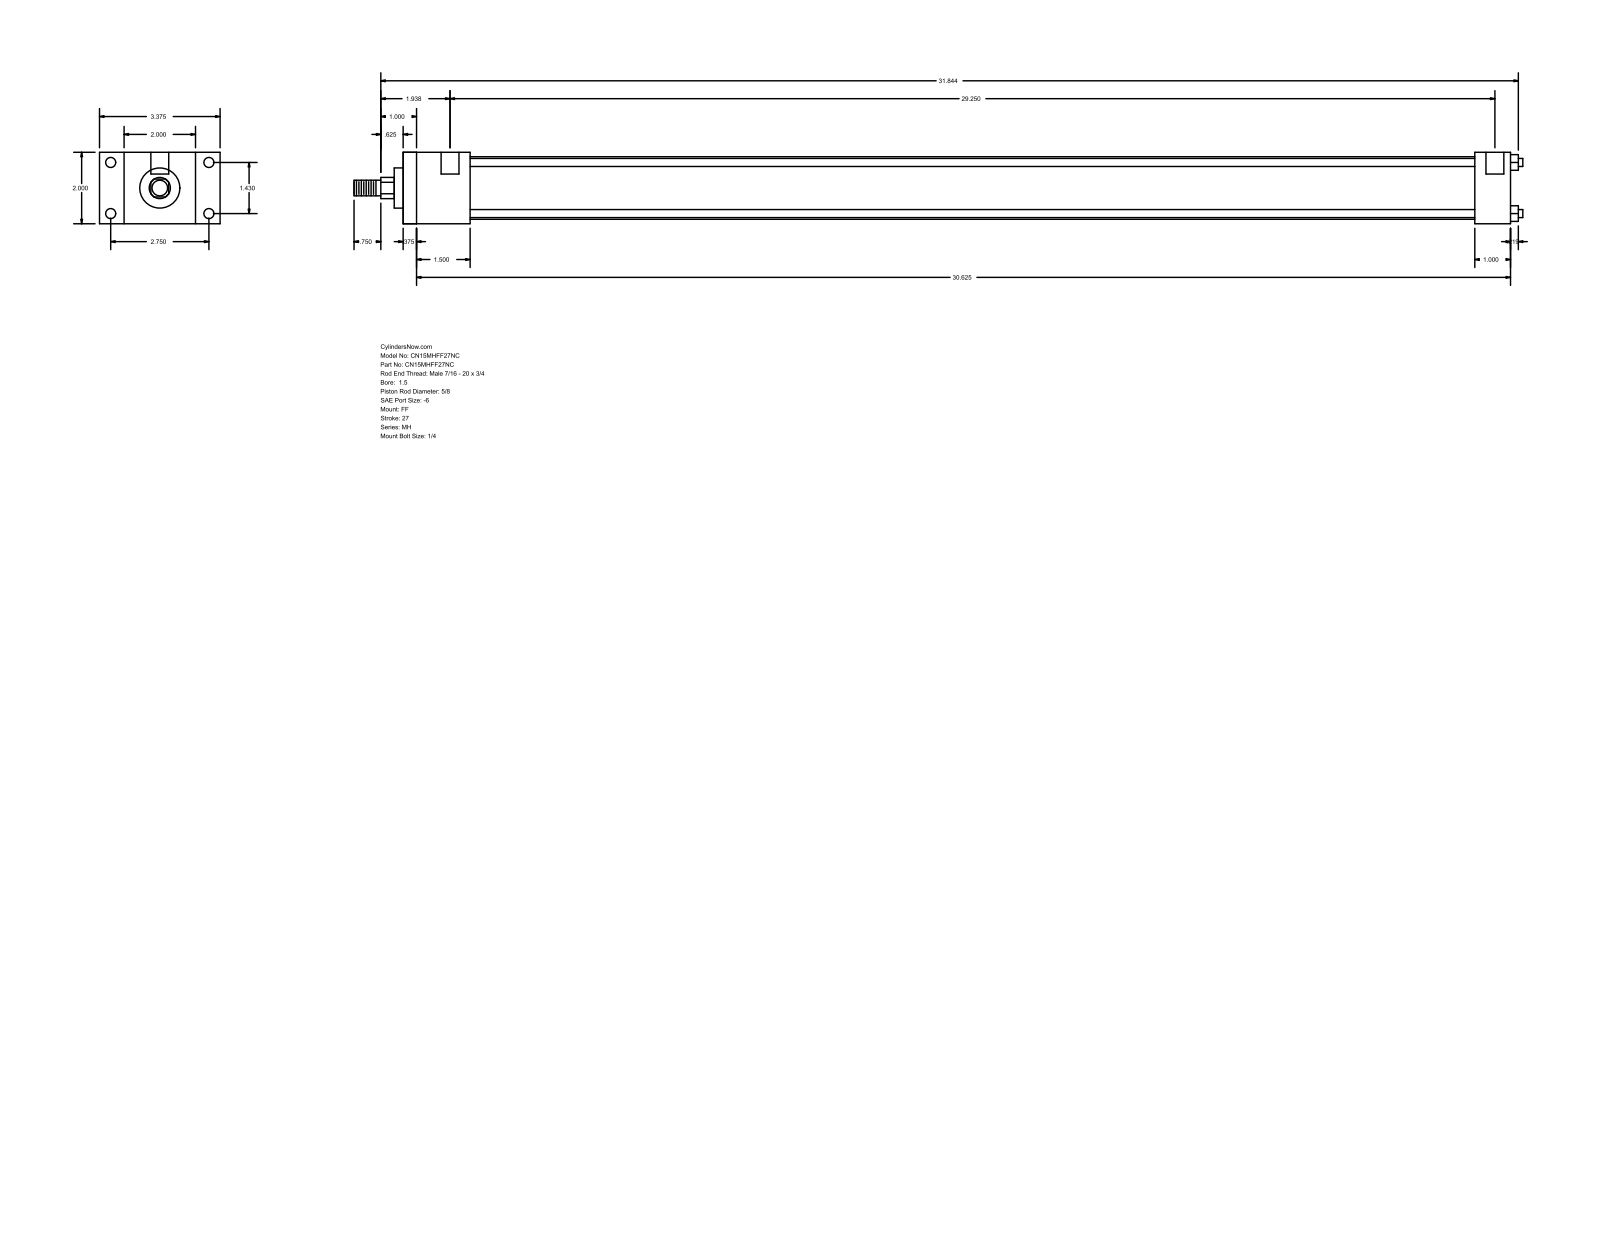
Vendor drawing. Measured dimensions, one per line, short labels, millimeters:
name: MH_FF__0150_0.625
written by: GSSL Pune (CONFIG_CONTROL_DESIGN)
unit: mm
bodies: 0 solids, 92 faces (64 planar, 28 cylindrical, 0 other)
size: 831.06 × 85.72 × 50.8
holes: 4× ⌀5.56, 4× ⌀7.14, 2× ⌀12.7
bosses: 4× ⌀5.71, 1× ⌀44.45, 1× ⌀28.57, 1× ⌀15.88, 1× ⌀11.11
rounds: 1× R7.54
face distances: 50.8, 787.39, 9.52, 777.87, 17.46, 68.26, 47.62, 38.1, 739.77, 762
hole spacings: 36.32, 69.84, 78.72, 746.12, 3.17, 742.95
